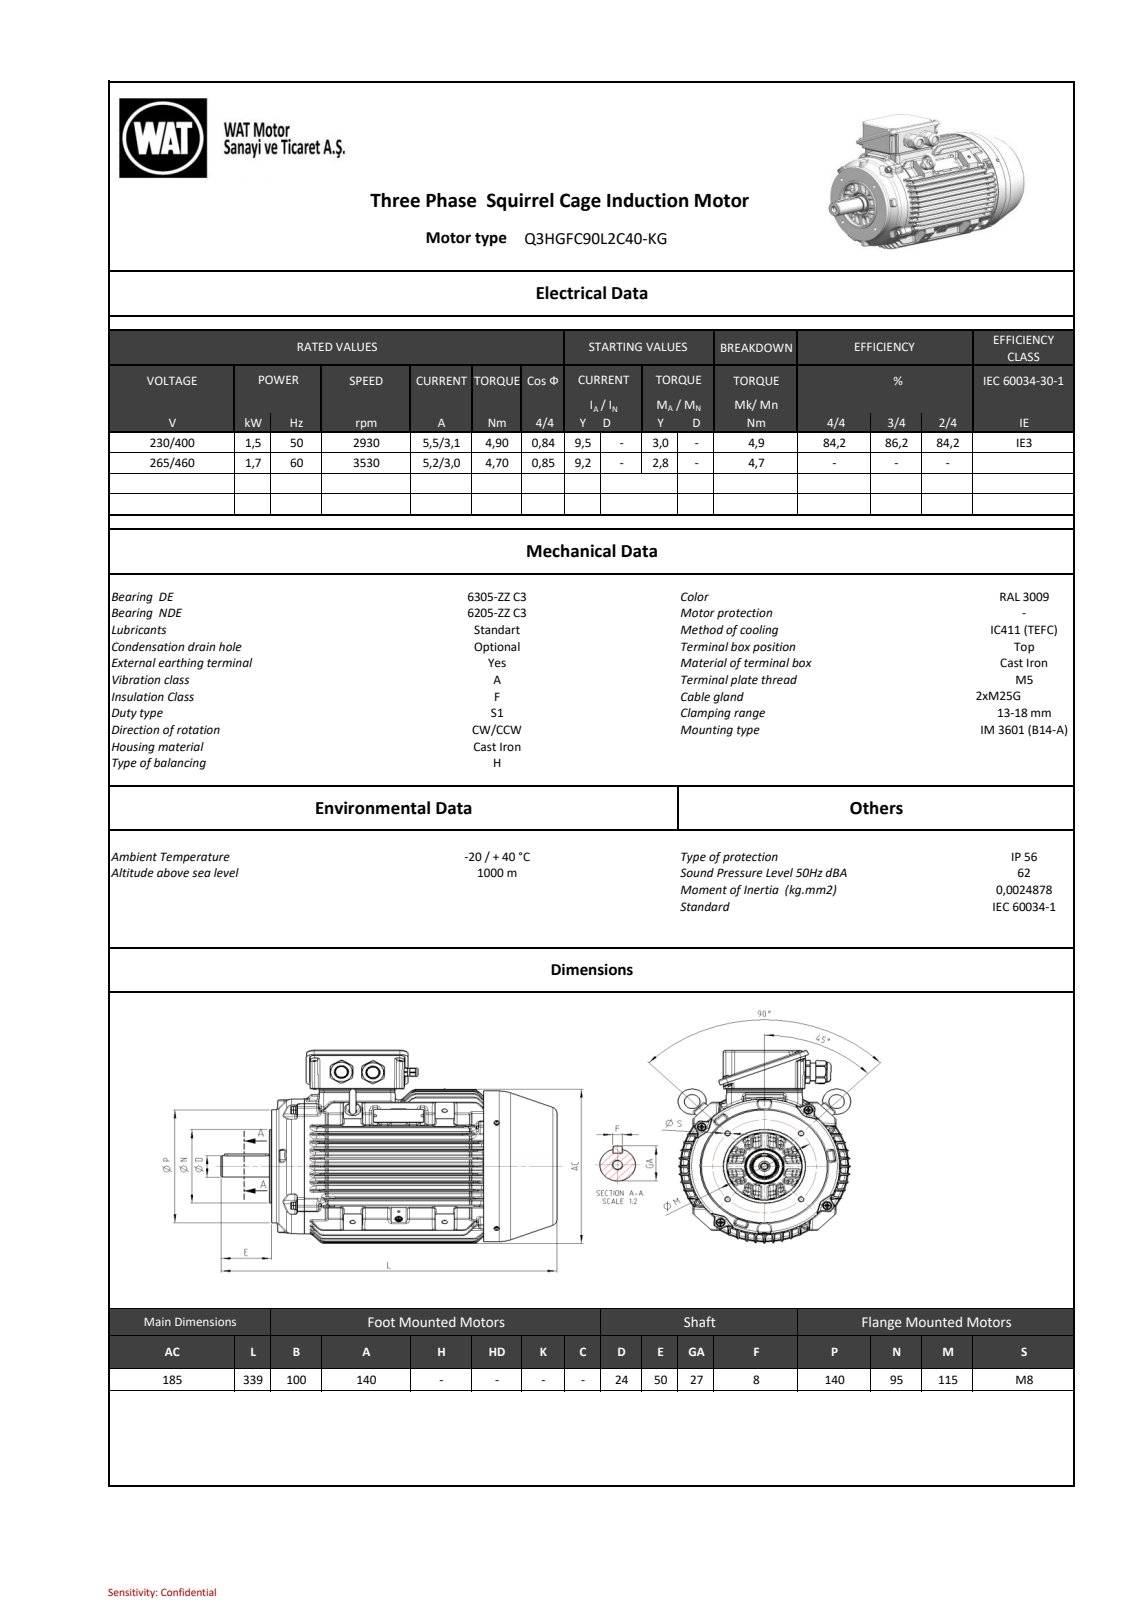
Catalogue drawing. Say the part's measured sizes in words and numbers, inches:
The part is named "260051B46F5629qs". Its 3-D file was written by "SIEMENS PLM Software NX 11.0 (AUTOMOTIVE_DESIGN)". It is 0 solids with 2830 faces: 802 planar, 811 cylindrical and 1217 other. Overall it measures 13.326 by 9.186 by 8.919 inches. Round holes: 5 of diameter 0.268, 3 of diameter 0.394, 2 of diameter 0.098, 2 of diameter 0.677, 1 of diameter 0.165, 1 of diameter 0.256, 1 of diameter 0.331, 1 of diameter 0.953, 1 of diameter 1.453, 1 of diameter 1.461, 1 of diameter 6.85. Round bosses or shafts: 4 of diameter 0.787, 3 of diameter 0.341, 3 of diameter 0.335, 3 of diameter 0.315, 3 of diameter 0.197, 2 of diameter 1.091, 2 of diameter 0.994, 2 of diameter 0.362. Partial cylindrical surfaces (rounded edges, fillets, slot ends): 254 of radius 0.059, 44 of radius 0.157, 37 of radius 0.02, 34 of radius 0.039, 24 of radius 0.079, 20 of radius 0.071, 18 of radius 0.008, 12 of radius 0.118. The main face-to-face distances are 0.474, 9.397, 0.118, 1.96, 11.357, 2.464, 0.119, 0.473, 0.476, 2.346. The hole center spacings are 3.201, 2.263, 4.527, 1.575, 2.264, 2.784, 2.952, 3.749.
